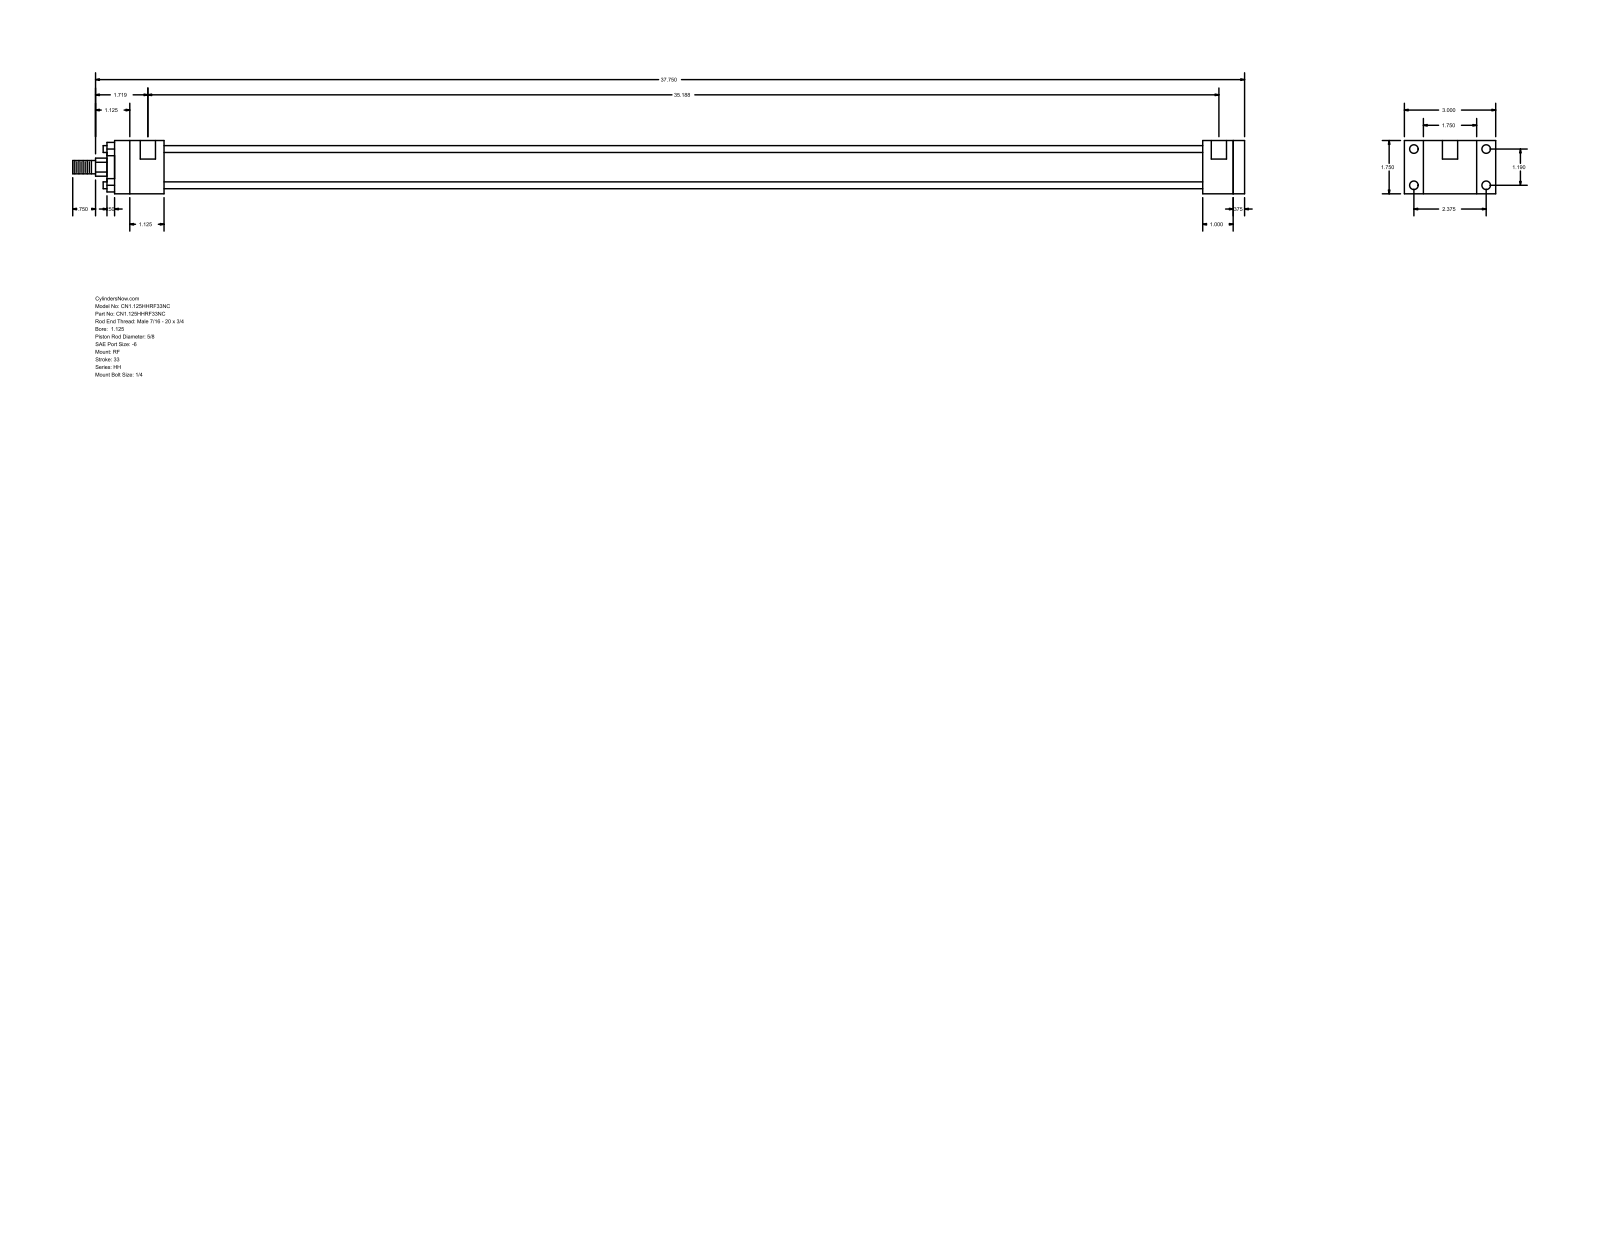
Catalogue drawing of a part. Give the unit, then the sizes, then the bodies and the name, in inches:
Units: inches
Overall size (bounding box): 38.5 × 3 × 1.75
Round holes (diameter × count): ⌀0.219 ×4, ⌀0.281 ×4, ⌀0.5 ×2
Round bosses / shafts (diameter × count): ⌀0.225 ×4, ⌀1.375 ×1, ⌀1.125 ×1, ⌀0.625 ×1, ⌀0.437 ×1
Partial cylindrical surfaces — rounded edges, fillets, slot ends (radius × count): R0.297 ×1
Main face-to-face distances: 1.75, 0.375, 1.375, 37.125, 0.625, 35.125, 35.5, 34.125, 1, 1.625
Hole centre spacings: 1.19, 2.375, 2.656, 35.063, 0.125, 35.187
Bodies: 0 solids, 92 faces (64 planar, 28 cylindrical, 0 other)
Part name (STEP PRODUCT): HH_RF__0112_0.625
STEP written by: GSSL Pune (CONFIG_CONTROL_DESIGN)
